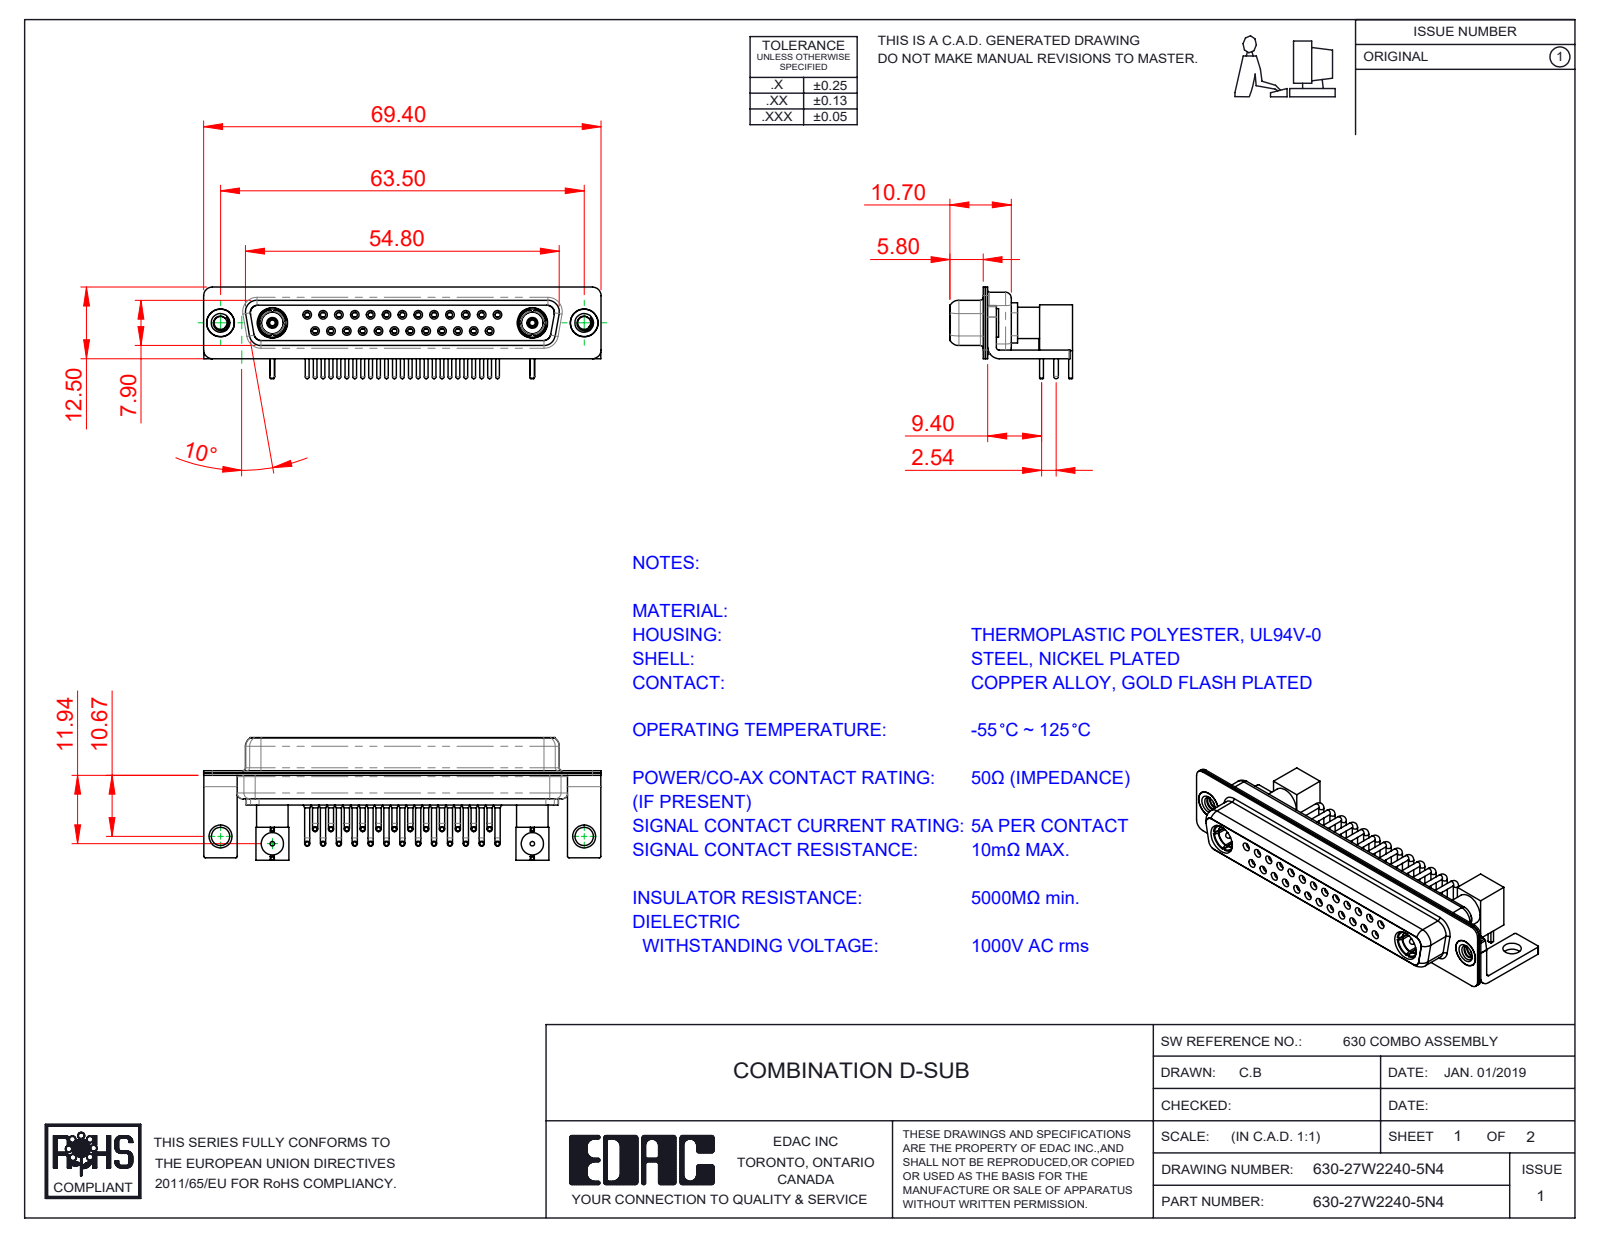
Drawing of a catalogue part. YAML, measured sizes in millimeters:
part_name: "630Combo Shell Front_37 Contacts; Co-Ax Plug Assy_RA; 630Combo Shell Rear_37 Contacts; RA Back Shell (+8 more)"
step_written_by: "SolidWorks 2020 (CONFIG_CONTROL_DESIGN)"
units: millimeters
bodies: {solids: 44, faces: 1980, planar: 596, cylindrical: 860, other: 524}
overall_size: [69.4, 21.41, 16]
volume: 6274
surface_area: 14381
round_holes:
  - {diameter: 1.1, count: 27}
  - {diameter: 1.5, count: 27}
  - {diameter: 0.9, count: 25}
  - {diameter: 2, count: 25}
  - {diameter: 1.7, count: 13}
  - {diameter: 1.6, count: 12}
  - {diameter: 4.85, count: 4}
  - {diameter: 0.8, count: 2}
  - {diameter: 2.26, count: 2}
  - {diameter: 2.83, count: 2}
  - {diameter: 3.1, count: 2}
  - {diameter: 3.2, count: 2}
round_bosses_or_shafts:
  - {diameter: 0.9, count: 26}
  - {diameter: 0.65, count: 25}
  - {diameter: 1.6, count: 14}
  - {diameter: 5, count: 4}
  - {diameter: 5.5, count: 2}
  - {diameter: 5.2, count: 2}
  - {diameter: 4.95, count: 2}
  - {diameter: 4.8, count: 2}
partial_cylinders:
  - {radius: 0.25, count: 16}
  - {radius: 1.5, count: 16}
  - {radius: 2, count: 13}
  - {radius: 1.35, count: 8}
  - {radius: 1.6, count: 8}
  - {radius: 0.5, count: 5}
  - {radius: 0.6, count: 4}
  - {radius: 0.65, count: 4}
face_to_face_distances: [0.4, 1.4, 0.45, 8.45, 1.8, 8.9, 6.2, 7.05, 0.8, 1.35]
hole_center_spacings: [3.16, 2.77, 5.54, 8.31, 5.03, 7.48, 11.08, 5.04]
